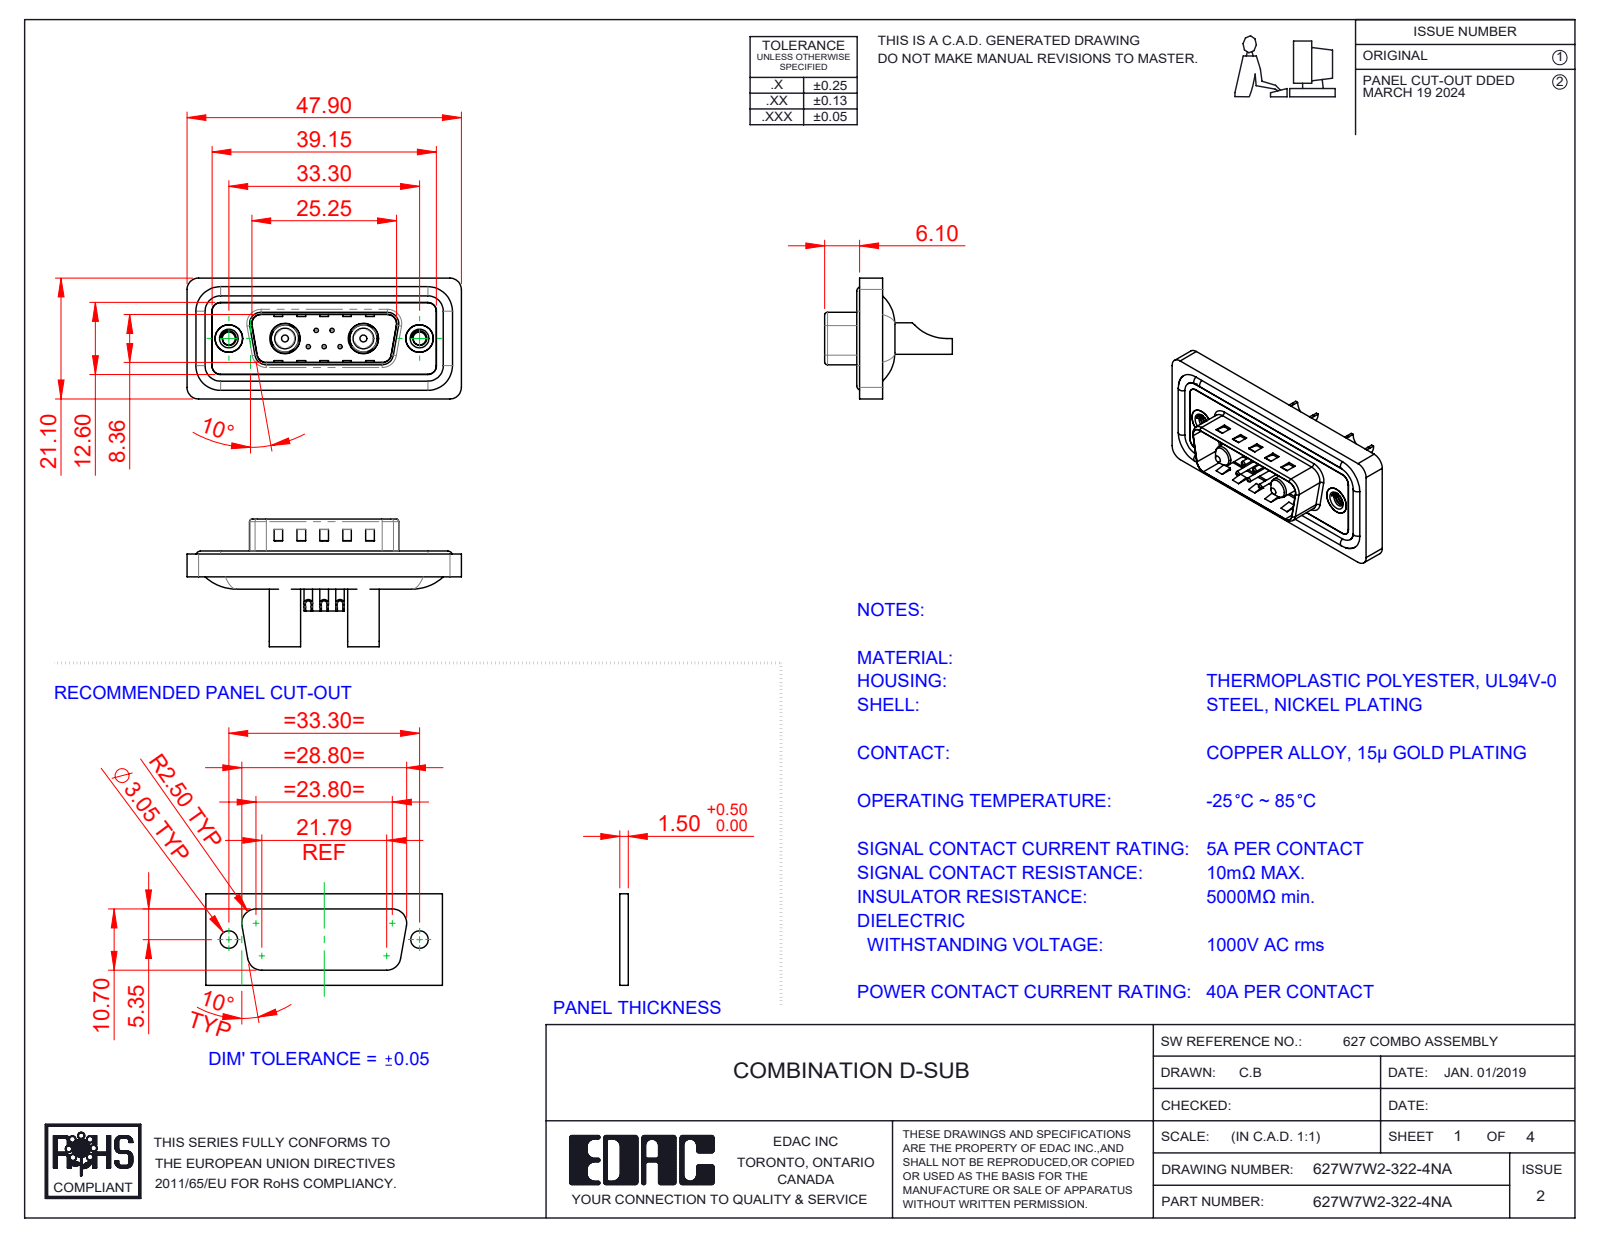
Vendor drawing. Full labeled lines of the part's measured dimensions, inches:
Part name (STEP PRODUCT): 627Combo Threaded Rivet_A; 627Combo Contact Row 1_22; Power Pin_40A SC; 627Combo Shell Rear_15 Contacts (+5 more)
STEP written by: SolidWorks 2023 (CONFIG_CONTROL_DESIGN)
Units: inches
Bodies: 16 solids, 716 faces (246 planar, 306 cylindrical, 164 other)
Overall size (bounding box): 1.886 × 0.878 × 0.831
Volume: 0.342 in³ · Surface area: 14.12 in²
Round holes (diameter × count): ⌀0.03 ×5, ⌀0.039 ×5, ⌀0.063 ×5, ⌀0.079 ×5, ⌀0.089 ×2, ⌀0.157 ×2, ⌀0.181 ×2, ⌀0.189 ×2, ⌀0.191 ×2, ⌀0.197 ×2, ⌀0.209 ×2
Round bosses / shafts (diameter × count): ⌀0.059 ×5, ⌀0.063 ×4, ⌀0.217 ×2, ⌀0.205 ×2, ⌀0.193 ×2, ⌀0.187 ×2, ⌀0.148 ×2, ⌀0.142 ×2
Partial cylindrical surfaces — rounded edges, fillets, slot ends (radius × count): R0.059 ×26, R0.079 ×20, R0.02 ×8, R0.063 ×8, R0.039 ×6, R0.01 ×4, R0.024 ×4, R0.026 ×4
Main face-to-face distances: 0.016, 0.043, 0.063, 0.02, 0.059, 0.122, 0.114, 0.032, 0.377, 0.098
Hole centre spacings: 0.124, 0.109, 0.386, 0.925, 0.17, 0.17, 0.198, 0.198
